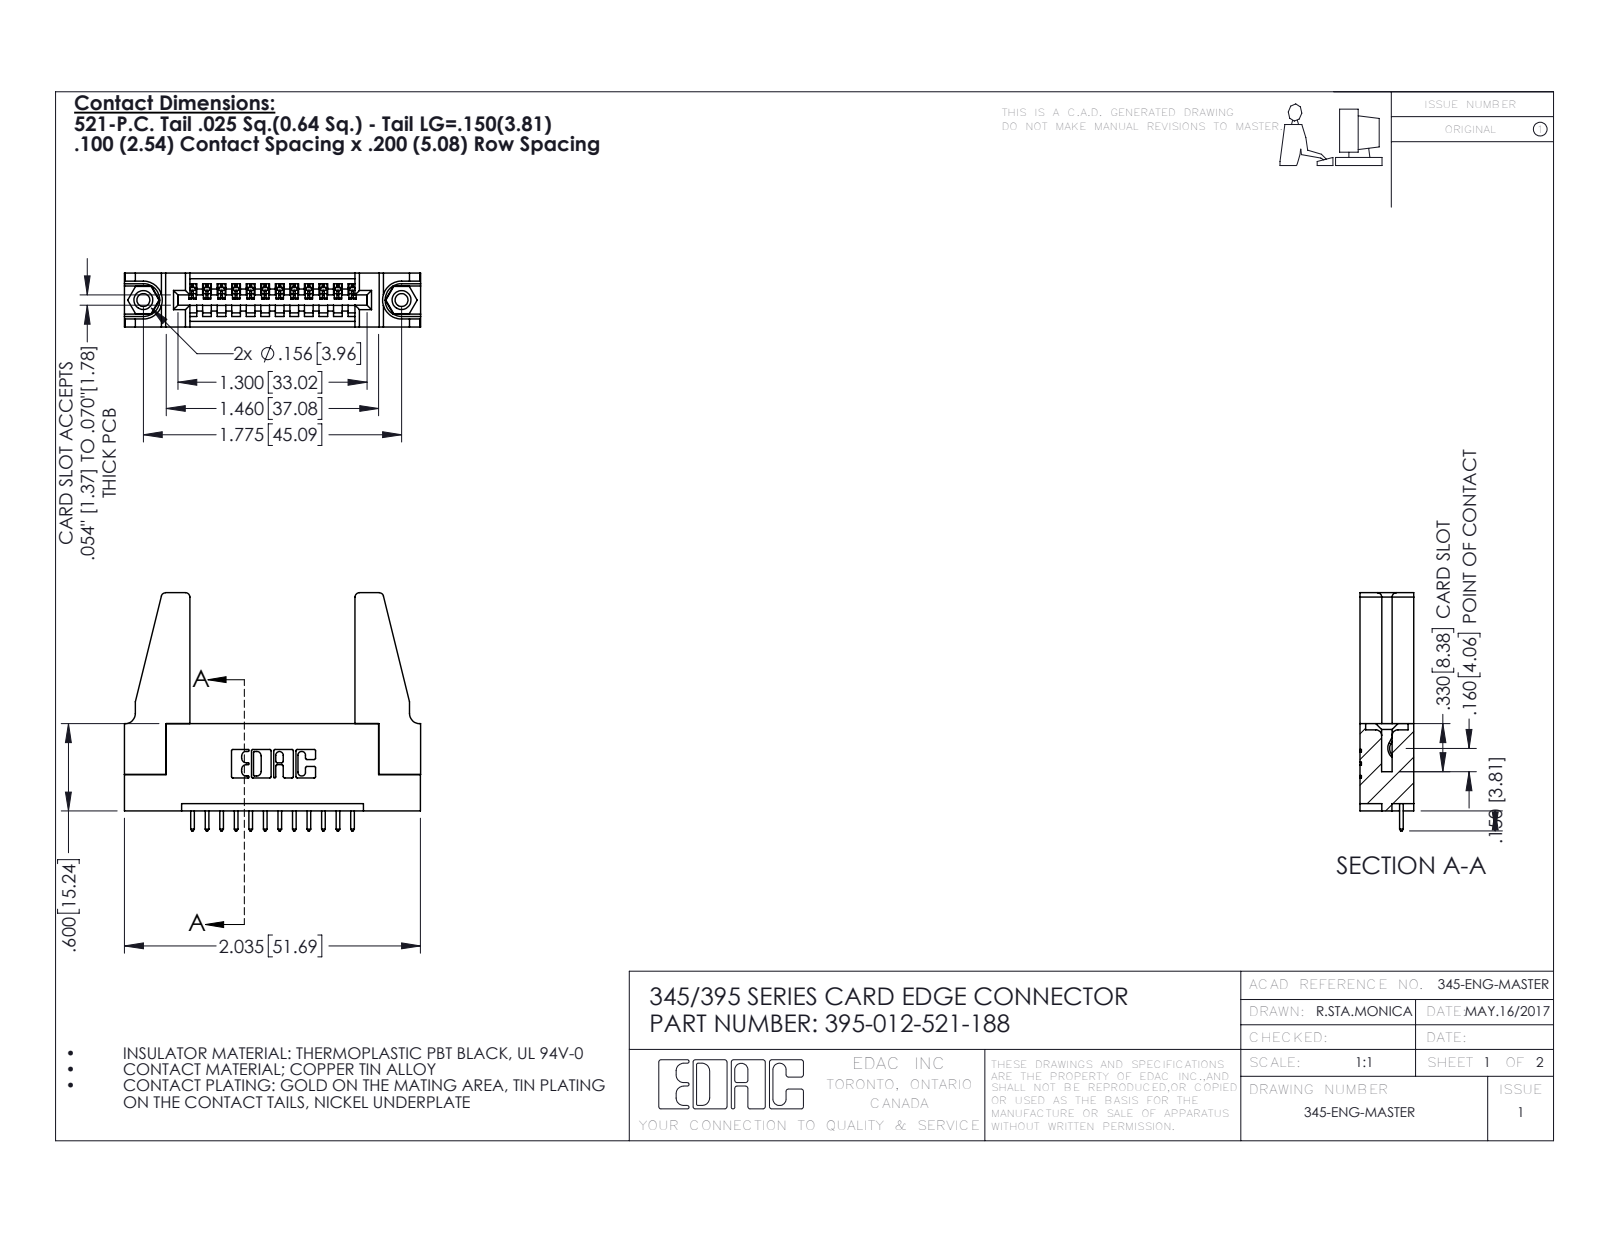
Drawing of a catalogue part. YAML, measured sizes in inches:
part_name: "345-220-078_345-220-088; 395-012-521-188; 345-292-001_345-293-121; 345-250-001_345-250-001-102 (+1 more)"
step_written_by: "SolidWorks 2016 (CONFIG_CONTROL_DESIGN)"
units: inches
bodies: {solids: 17, faces: 946, planar: 632, cylindrical: 298, other: 16}
overall_size: [2.036, 1.637, 0.37]
volume: 0.481
surface_area: 13.55
round_holes:
  - {diameter: 0.089, count: 2}
  - {diameter: 0.125, count: 2}
  - {diameter: 0.156, count: 2}
  - {diameter: 0.064, count: 1}
round_bosses_or_shafts:
  - {diameter: 0.155, count: 2}
partial_cylinders:
  - {radius: 0.006, count: 24}
  - {radius: 0.01, count: 24}
  - {radius: 0.01, count: 22}
  - {radius: 0.03, count: 8}
  - {radius: 0.007, count: 6}
  - {radius: 0.031, count: 6}
  - {radius: 0.026, count: 3}
  - {radius: 0.031, count: 2}
face_to_face_distances: [0.37, 0.072, 0.298, 0.2, 0.098, 0.272, 0.025, 0.225, 0.148, 0.15]
hole_center_spacings: [0.27, 1.543, 1.775]
